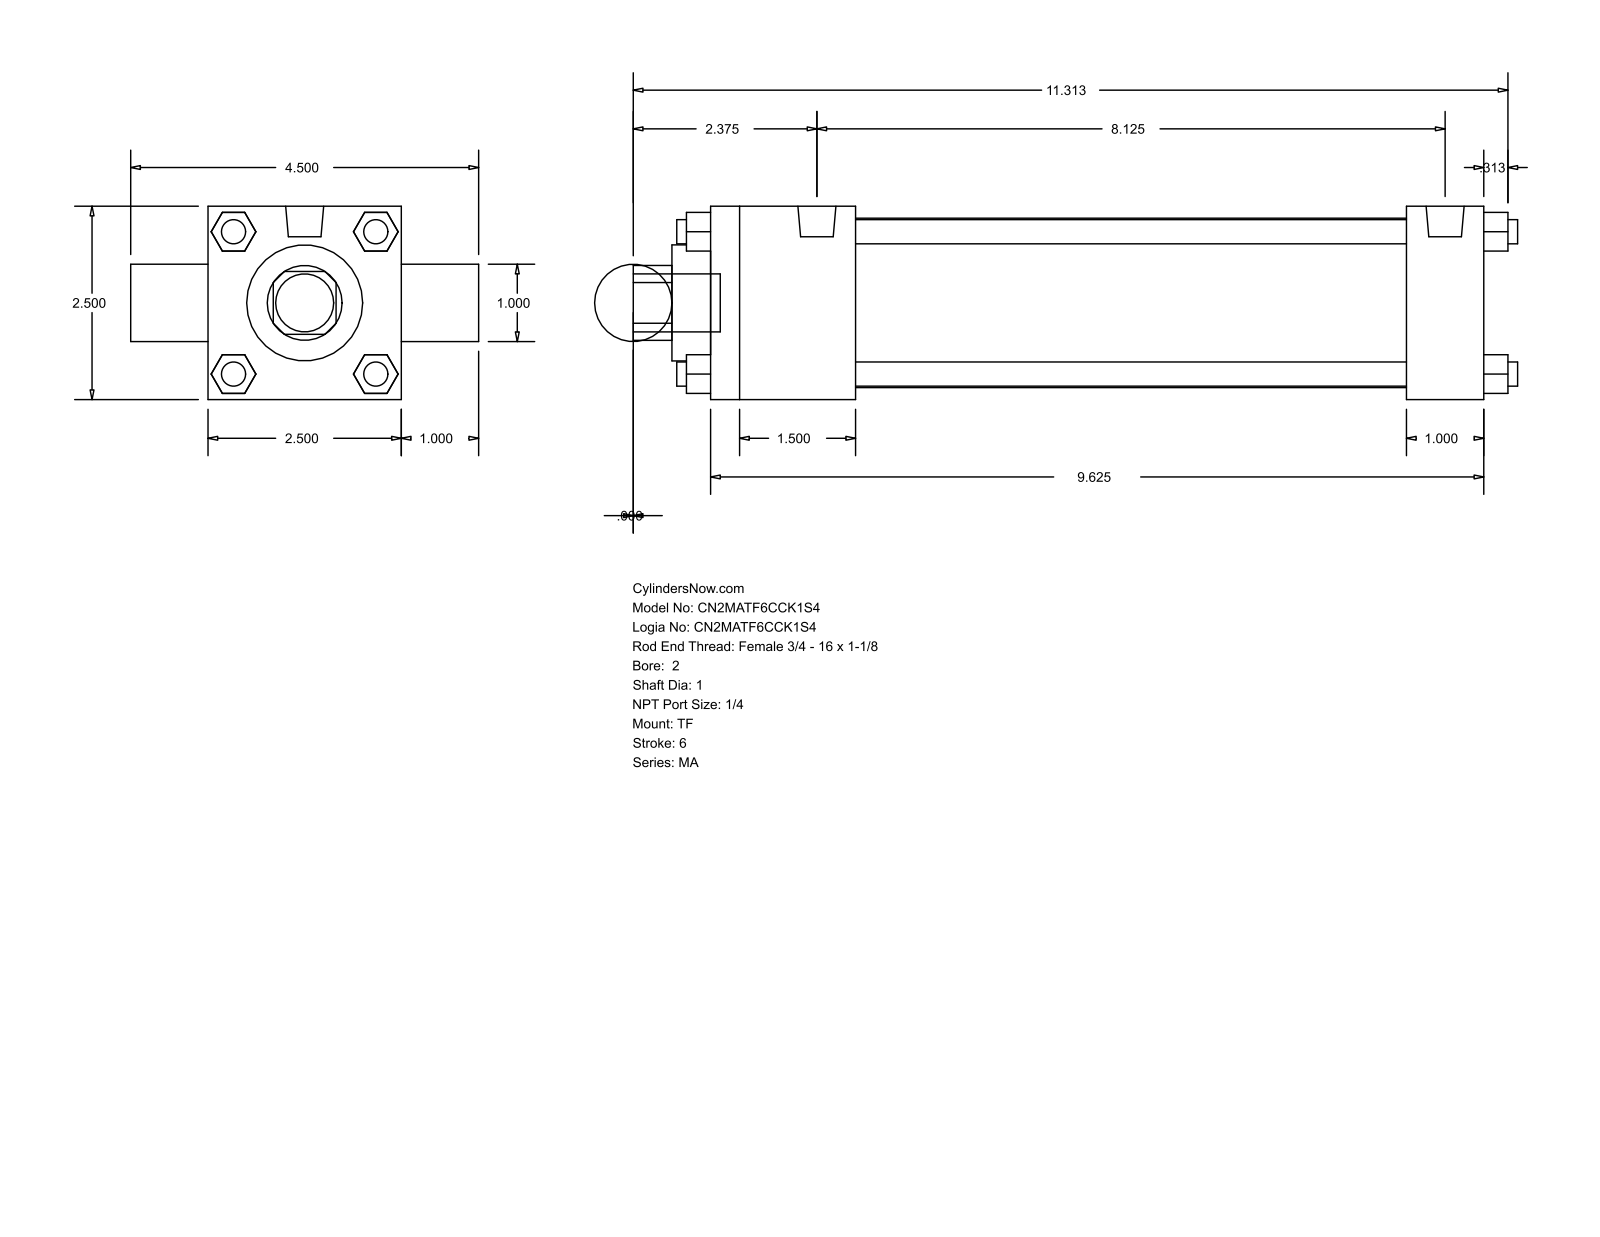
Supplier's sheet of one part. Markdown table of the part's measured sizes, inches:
| quantity | value |
| --- | --- |
| part name | MA_TF__0200_1 |
| STEP written by | GSSL Pune (CONFIG_CONTROL_DESIGN) |
| units | inches |
| bodies | 0 solids, 120 faces (92 planar, 28 cylindrical, 0 other) |
| overall size | 11.437 × 4.5 × 2.5 |
| round holes (diameter × count) | 1 × 2, 1.5 × 1, 2.19 × 1 |
| round bosses / shafts (diameter × count) | 0.313 × 7, 0.492 × 2, 0.75 × 1 |
| partial cylindrical surfaces (radius × count) | 0.484 × 1 |
| main face-to-face distances | 2.5, 1, 10, 0.5, 1.875, 9, 7.125, 8.125, 3.5, 1.593 |
